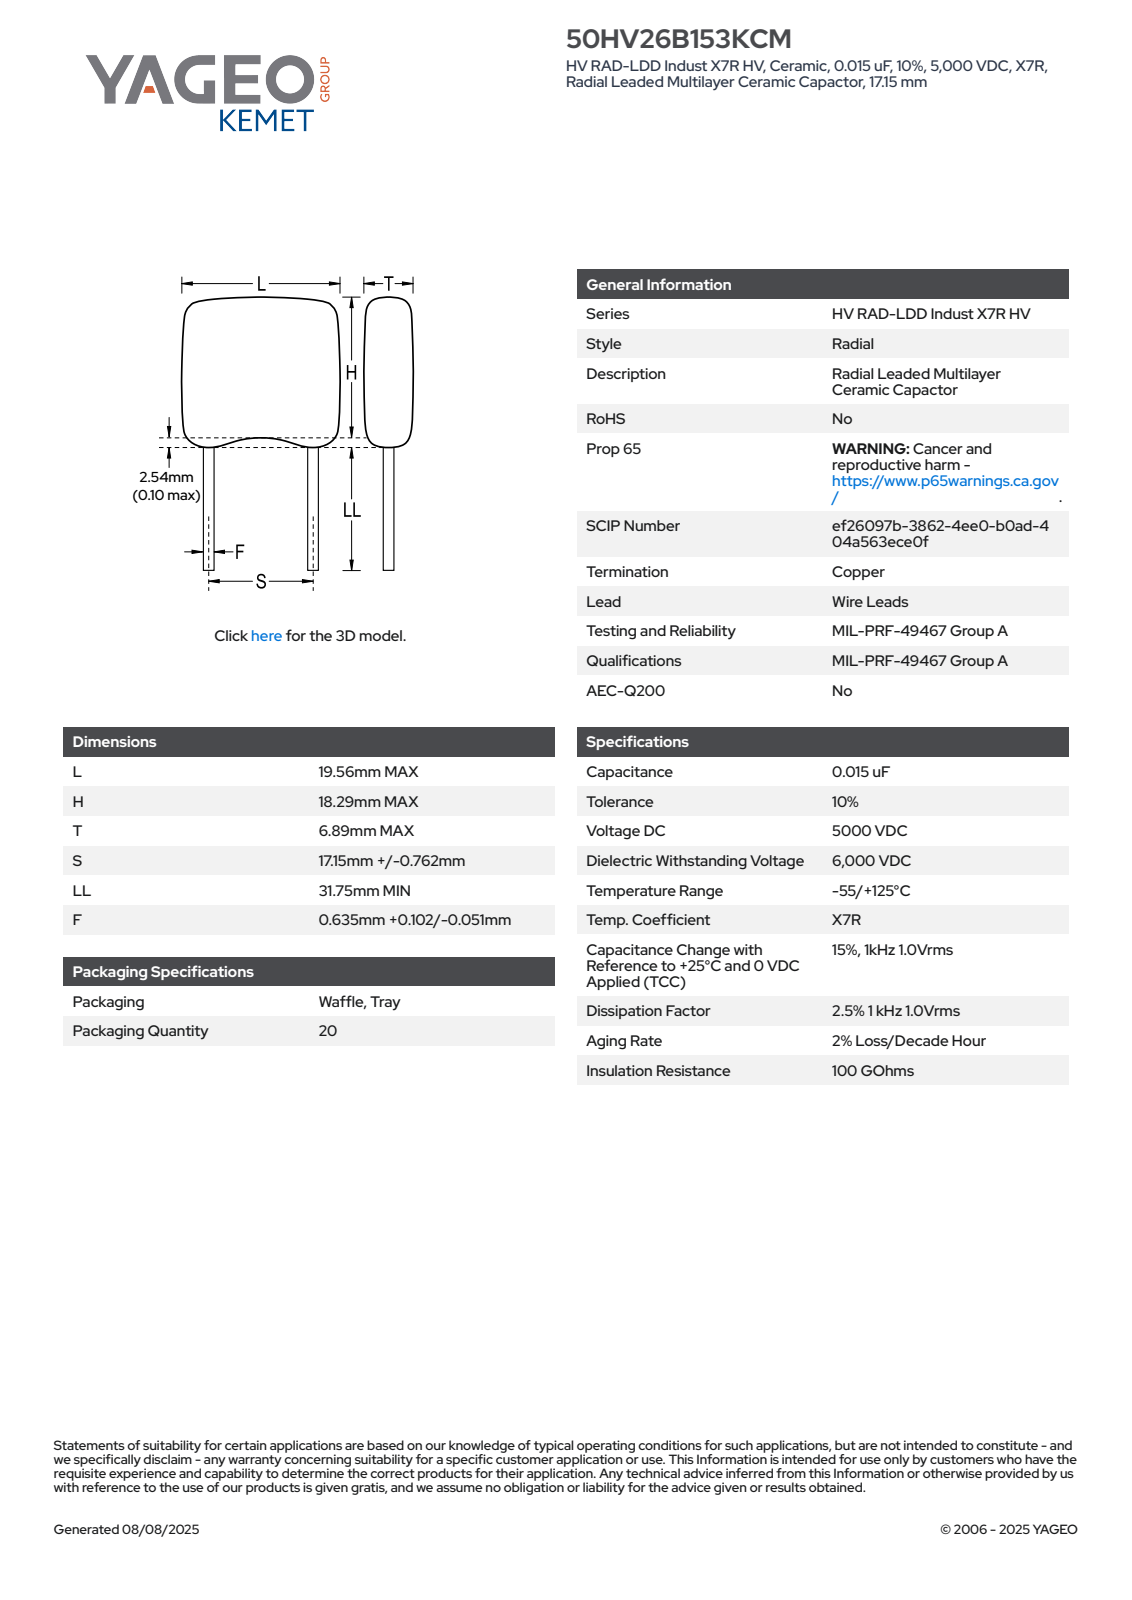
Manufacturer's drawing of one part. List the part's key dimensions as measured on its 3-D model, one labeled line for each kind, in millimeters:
Part name (STEP PRODUCT): CCRM_RCST_HV26_L19.56H18.29T6.89S17.15LL31.75F0.737
STEP written by: SolidWorks 2021 (AUTOMOTIVE_DESIGN)
Units: millimetres
Bodies: 4 solids, 98 faces (66 planar, 20 cylindrical, 12 other)
Overall size (bounding box): 23.05 × 19.56 × 6.89
Volume: 2 516 mm³ · Surface area: 1 275 mm²
Round bosses / shafts (diameter × count): ⌀0.74 ×2
Partial cylindrical surfaces — rounded edges, fillets, slot ends (radius × count): R1 ×8, R0.5 ×4
Main face-to-face distances: 6.89, 19.56, 19.87, 3.17, 23.04, 14.46, 11.29, 8.58, 11.97, 8.8
